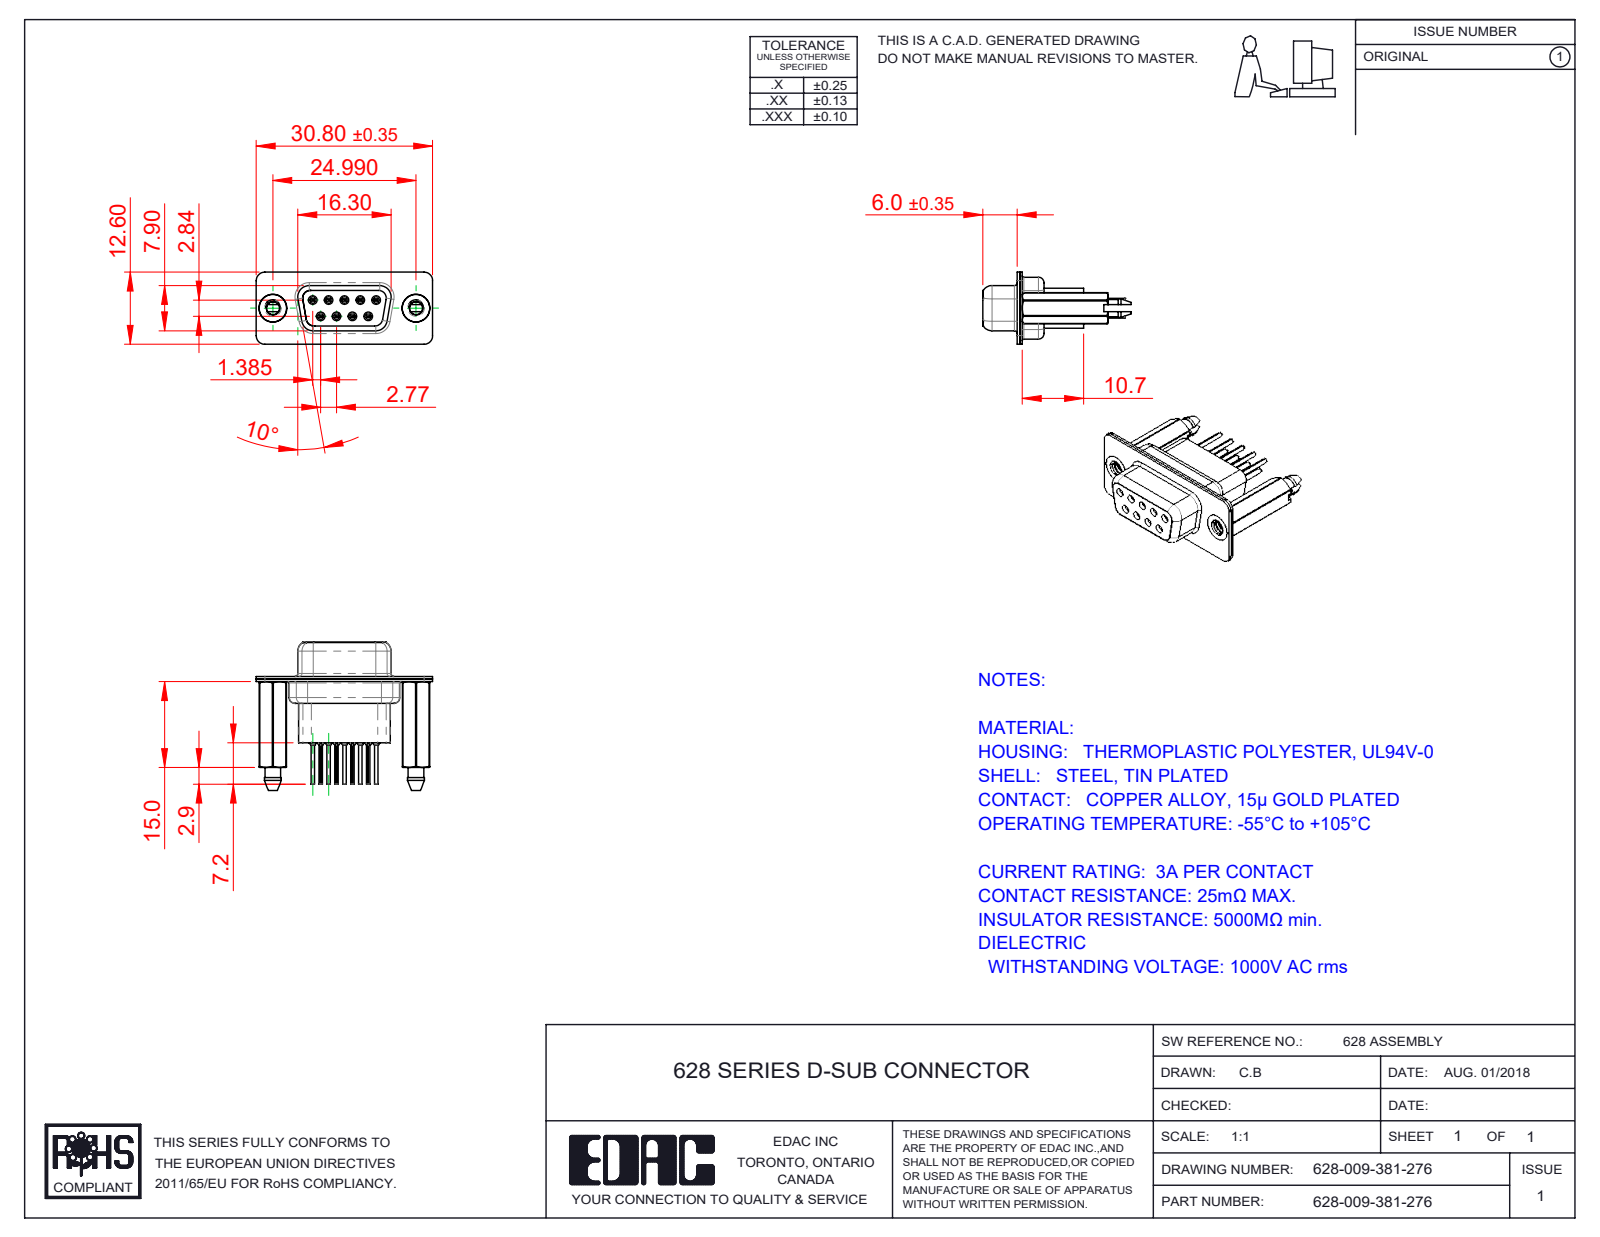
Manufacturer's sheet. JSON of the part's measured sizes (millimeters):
{"part_name": "628 Shell Front_09 Contacts; 628 Shell Rear_09 Contacts; 628 Contact Row 1_71; 628 Housing_09 HP (+3 more)", "step_written_by": "SolidWorks 2020 (CONFIG_CONTROL_DESIGN)", "units": "millimeters", "bodies": {"solids": 14, "faces": 1460, "planar": 378, "cylindrical": 466, "other": 616}, "overall_size": [30.8, 25.9, 12.6], "volume_mm3": 2635, "surface_area_mm2": 6123, "round_holes": [[0.2, 9], [0.8, 9], [0.9, 9], [1.1, 9], [1.6, 9], [1.7, 5], [2.26, 2], [4, 2], [4.05, 2], [4.85, 2]], "round_bosses_or_shafts": [[2, 9], [1.5, 9], [1.2, 9], [0.6, 9], [4.95, 2], [4.8, 2]], "partial_cylinders_radius": [[1.5, 19], [0.1, 18], [2, 12], [0.28, 9], [1.35, 6], [1.6, 6], [0.25, 4], [0.5, 4]], "face_to_face_distances": [0.45, 0.4, 0.9, 8.5, 6.6, 4.76, 1.9, 1.4, 7, 10.7], "hole_center_spacings": [3.16, 2.77, 5.54, 5.03, 5.04, 8.31, 7.48, 7.49]}
